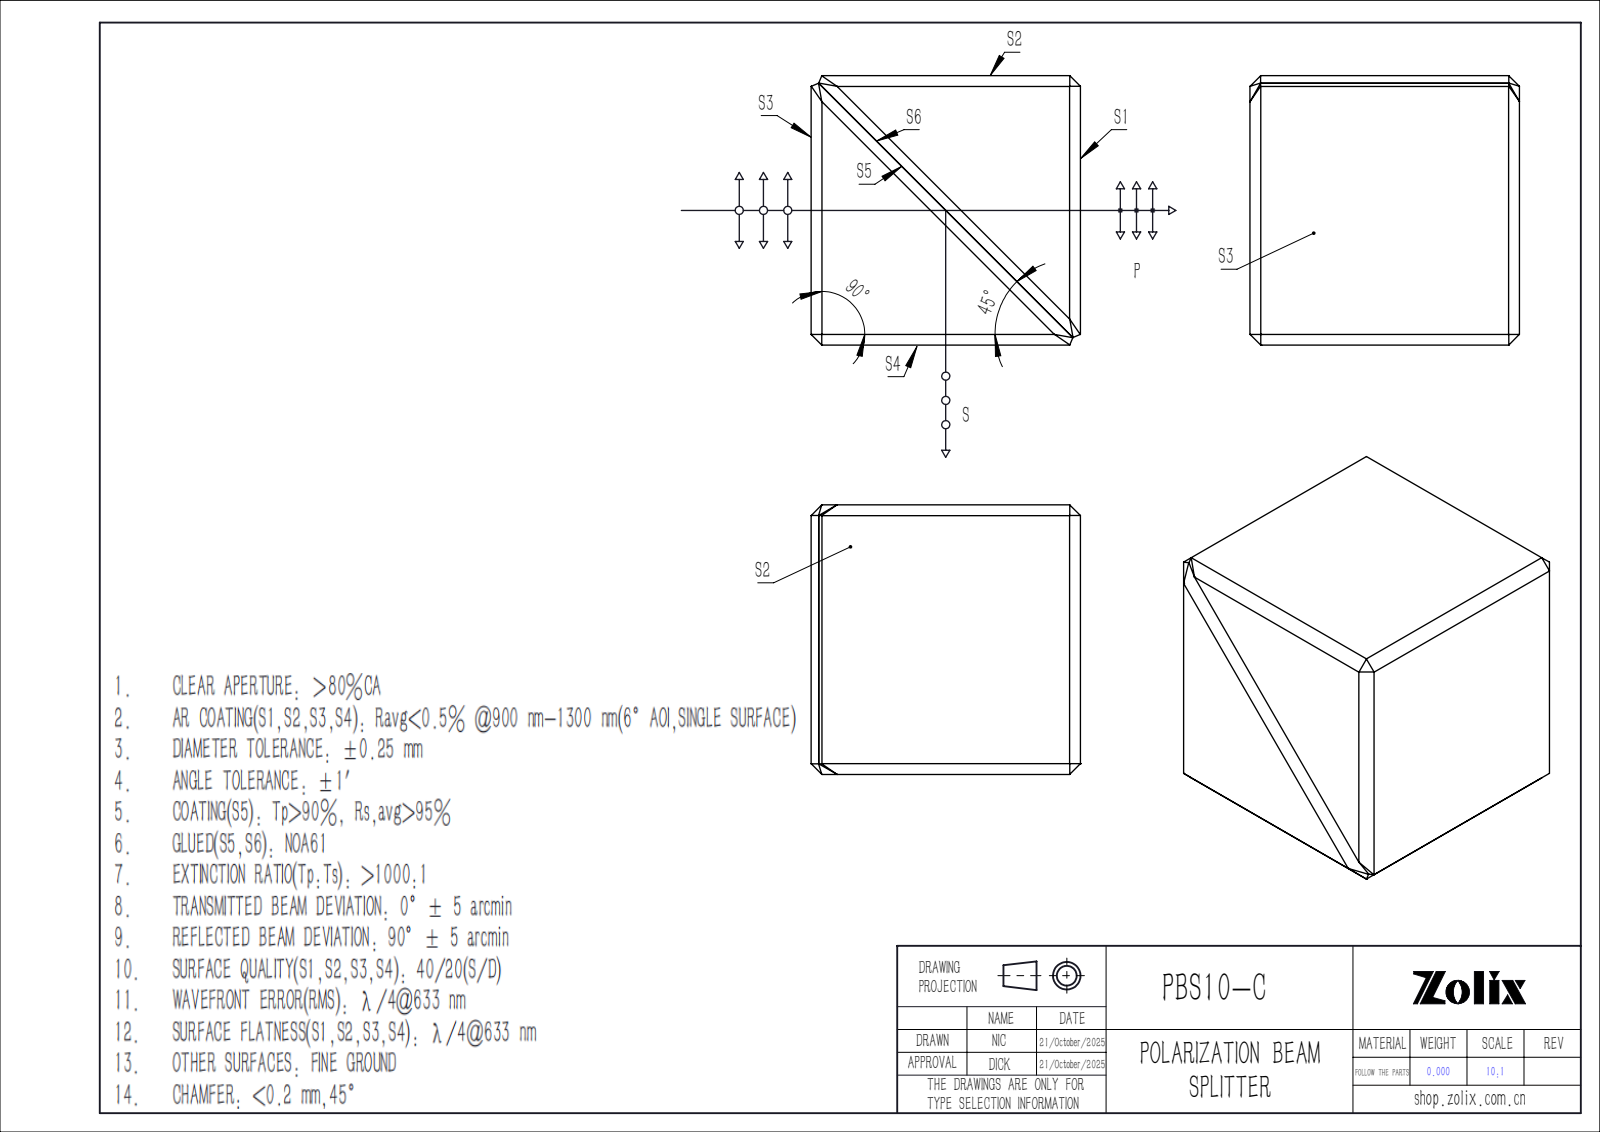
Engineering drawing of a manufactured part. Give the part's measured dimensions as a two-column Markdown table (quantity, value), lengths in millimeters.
| quantity | value |
| --- | --- |
| part name | PBS613-1; PBS613-1-2; PBS613-1-1 |
| STEP written by | SolidWorks 2022 (CONFIG_CONTROL_DESIGN) |
| units | millimeters |
| bodies | 2 solids, 43 faces (41 planar, 2 cylindrical, 0 other) |
| overall size | 10 × 10 × 10 |
| volume | 996 mm³ |
| surface area | 854 mm² |
| round holes (diameter × count) | 0.2 × 1 |
| main face-to-face distances | 10, 13.86, 6.79, 12.7, 6.93, 6.92, 13.85, 14.7, 16.85, 14.69 |
